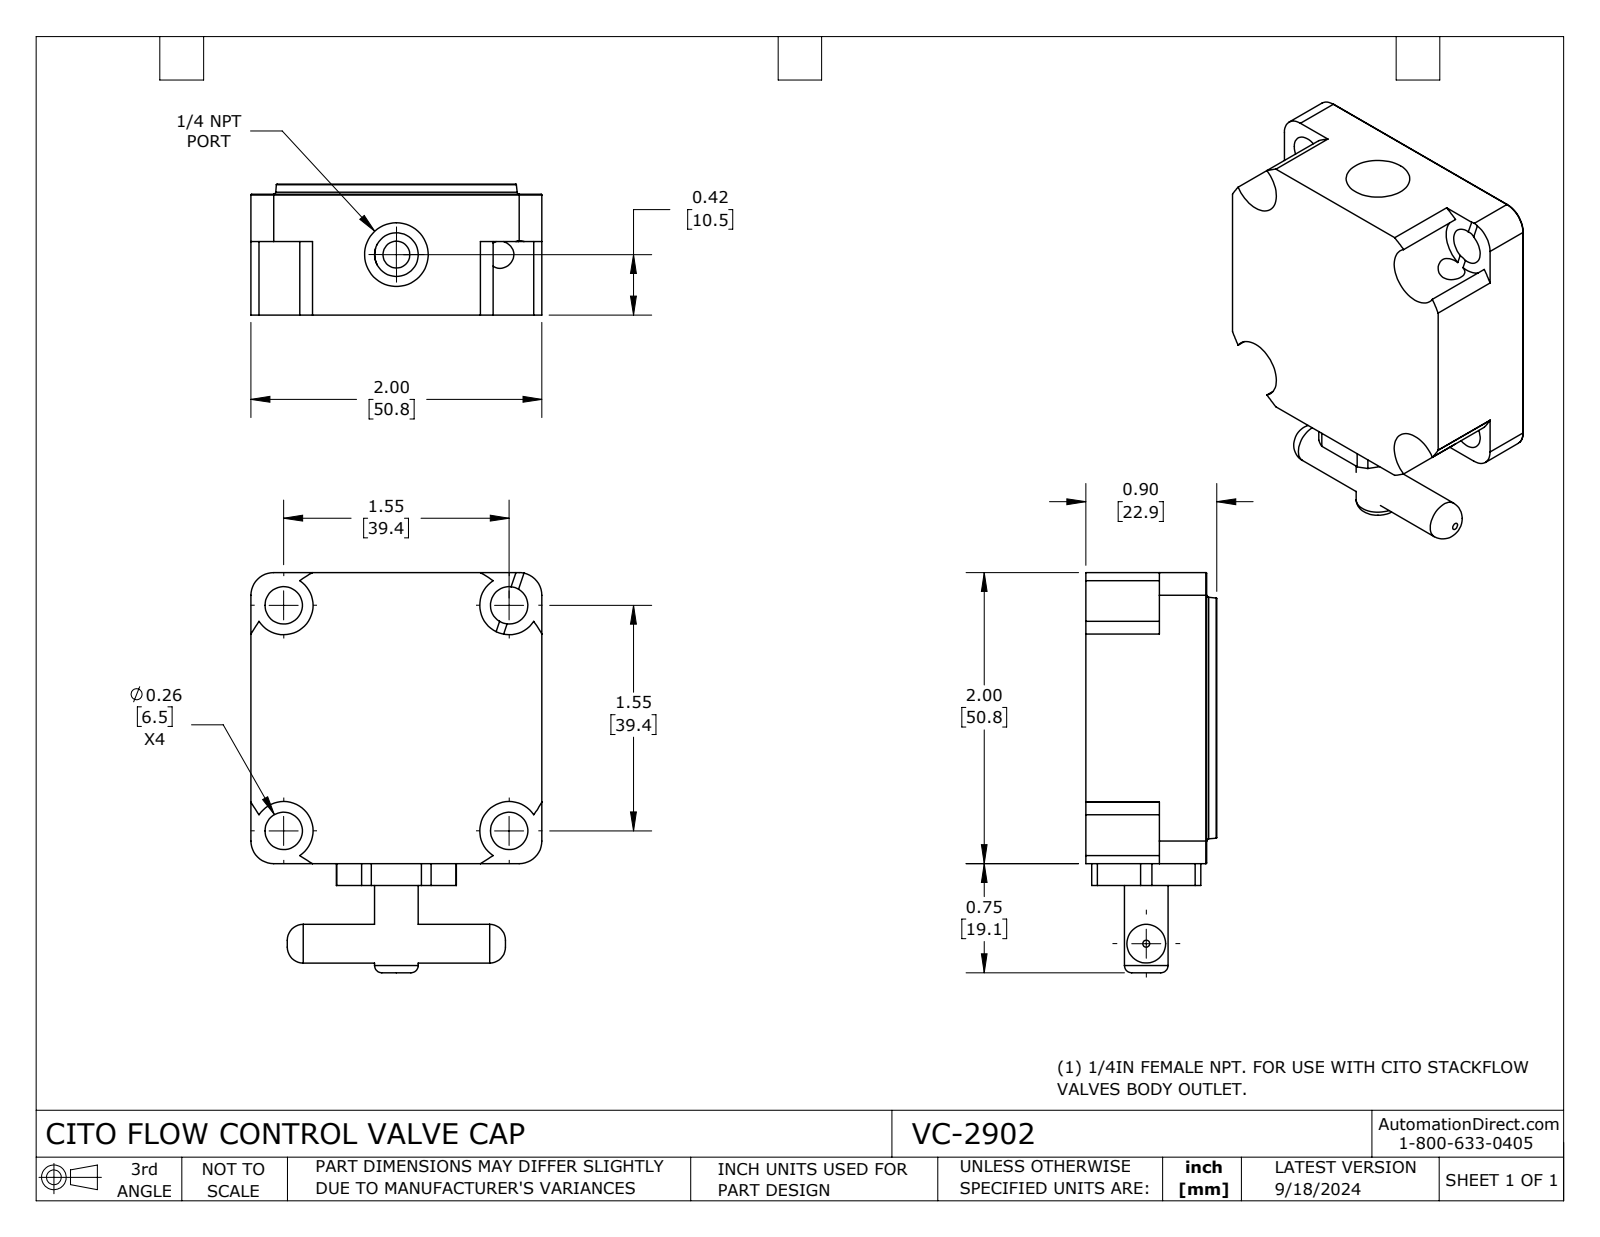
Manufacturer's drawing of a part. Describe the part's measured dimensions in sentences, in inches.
The part is named "VC-2902". Its 3-D file was written by "SolidWorks 2023 (CONFIG_CONTROL_DESIGN)". It is 4 solids with 165 faces: 34 planar, 85 cylindrical and 46 other. Overall it measures 2.75 by 2 by 0.9 inches. Its volume is 2.873 cubic inches and its surface area 24.57 square inches. Round holes: 4 of diameter 0.257, 2 of diameter 0.188, 1 of diameter 0.3, 1 of diameter 0.301, 1 of diameter 0.375, 1 of diameter 0.437, 1 of diameter 0.438. Round bosses or shafts: 1 of diameter 0.431, 1 of diameter 0.397, 1 of diameter 0.376, 1 of diameter 0.266. Partial cylindrical surfaces (rounded edges, fillets, slot ends): 5 of radius 0.005, 5 of radius 0.187, 4 of radius 0.156, 4 of radius 0.202, 1 of radius 0.217, 1 of radius 0.412, 1 of radius 1.155. The main face-to-face distances are 2, 0.9, 0.07, 0.83, 0.15, 2.15, 0.395, 0.325, 0.505, 0.68. The hole center spacings are 1.096, 1.55, 2.191.
